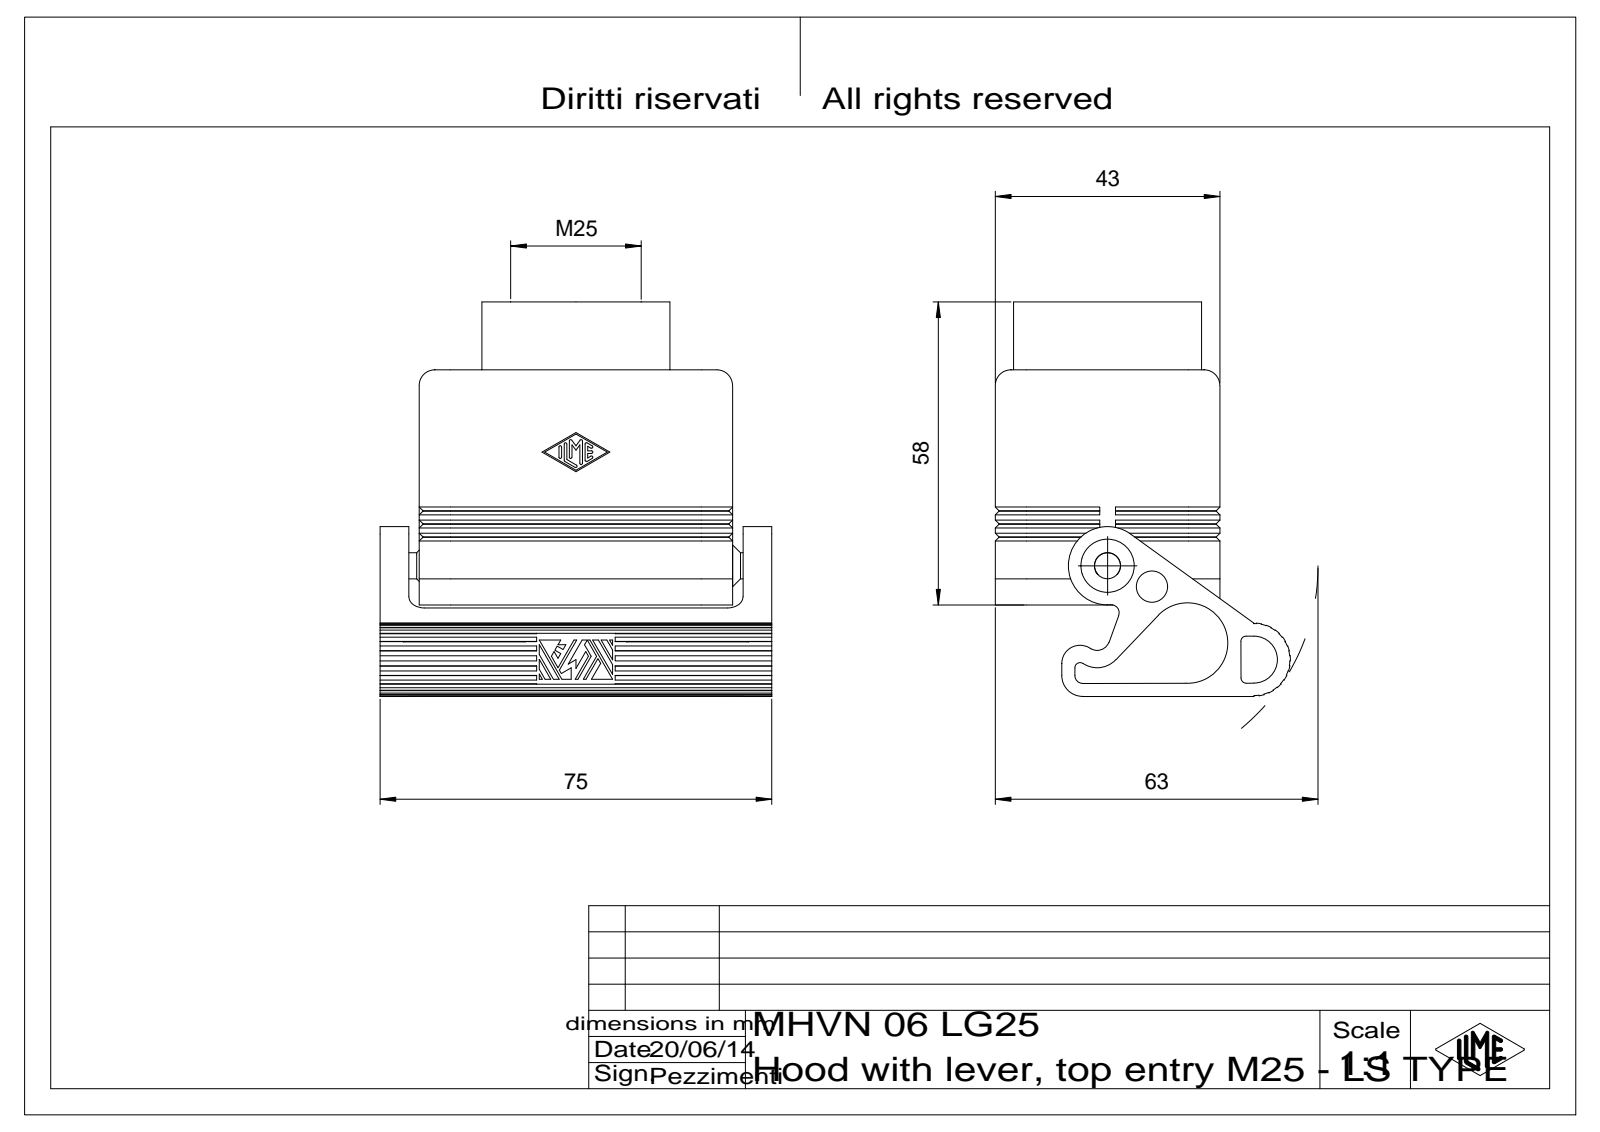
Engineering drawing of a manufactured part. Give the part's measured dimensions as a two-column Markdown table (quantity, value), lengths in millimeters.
| quantity | value |
| --- | --- |
| part name | MFVN_06_LG25; MFVN_06_LG25.stp; CHV_T\\S\\\|llengeh\\S\\duse_1_B\\S\\\|gel_f\\S\\\|r_einen_Einsatz; MHV_06_LG25.stp (+1 more) |
| STEP written by | Creo Elements/Direct Modeling 18.0B 02-Dec-2011 (C) Parametric Technology GmbH (AUTOMOTIVE_DESIGN) |
| units | millimeters |
| bodies | 2 solids, 626 faces (343 planar, 203 cylindrical, 80 other) |
| overall size | 75.19 × 75 × 62.02 |
| volume | 57 778 mm³ |
| surface area | 33 964 mm² |
| round holes (diameter × count) | 2.46 × 4, 4 × 4, 6 × 1, 10.2 × 1, 23 × 1, 25 × 1 |
| round bosses / shafts (diameter × count) | 36 × 1, 5 × 1 |
| partial cylindrical surfaces (radius × count) | 0.25 × 14, 0.8 × 10, 3 × 10, 1 × 8, 0.9 × 6, 2 × 4, 3 × 4, 5.3 × 4 |
| main face-to-face distances | 3, 40, 37, 8.5, 5, 62, 57, 43, 11.5, 2 |
| hole center spacings | 25.81, 27, 44, 51.62, 9.39 |
